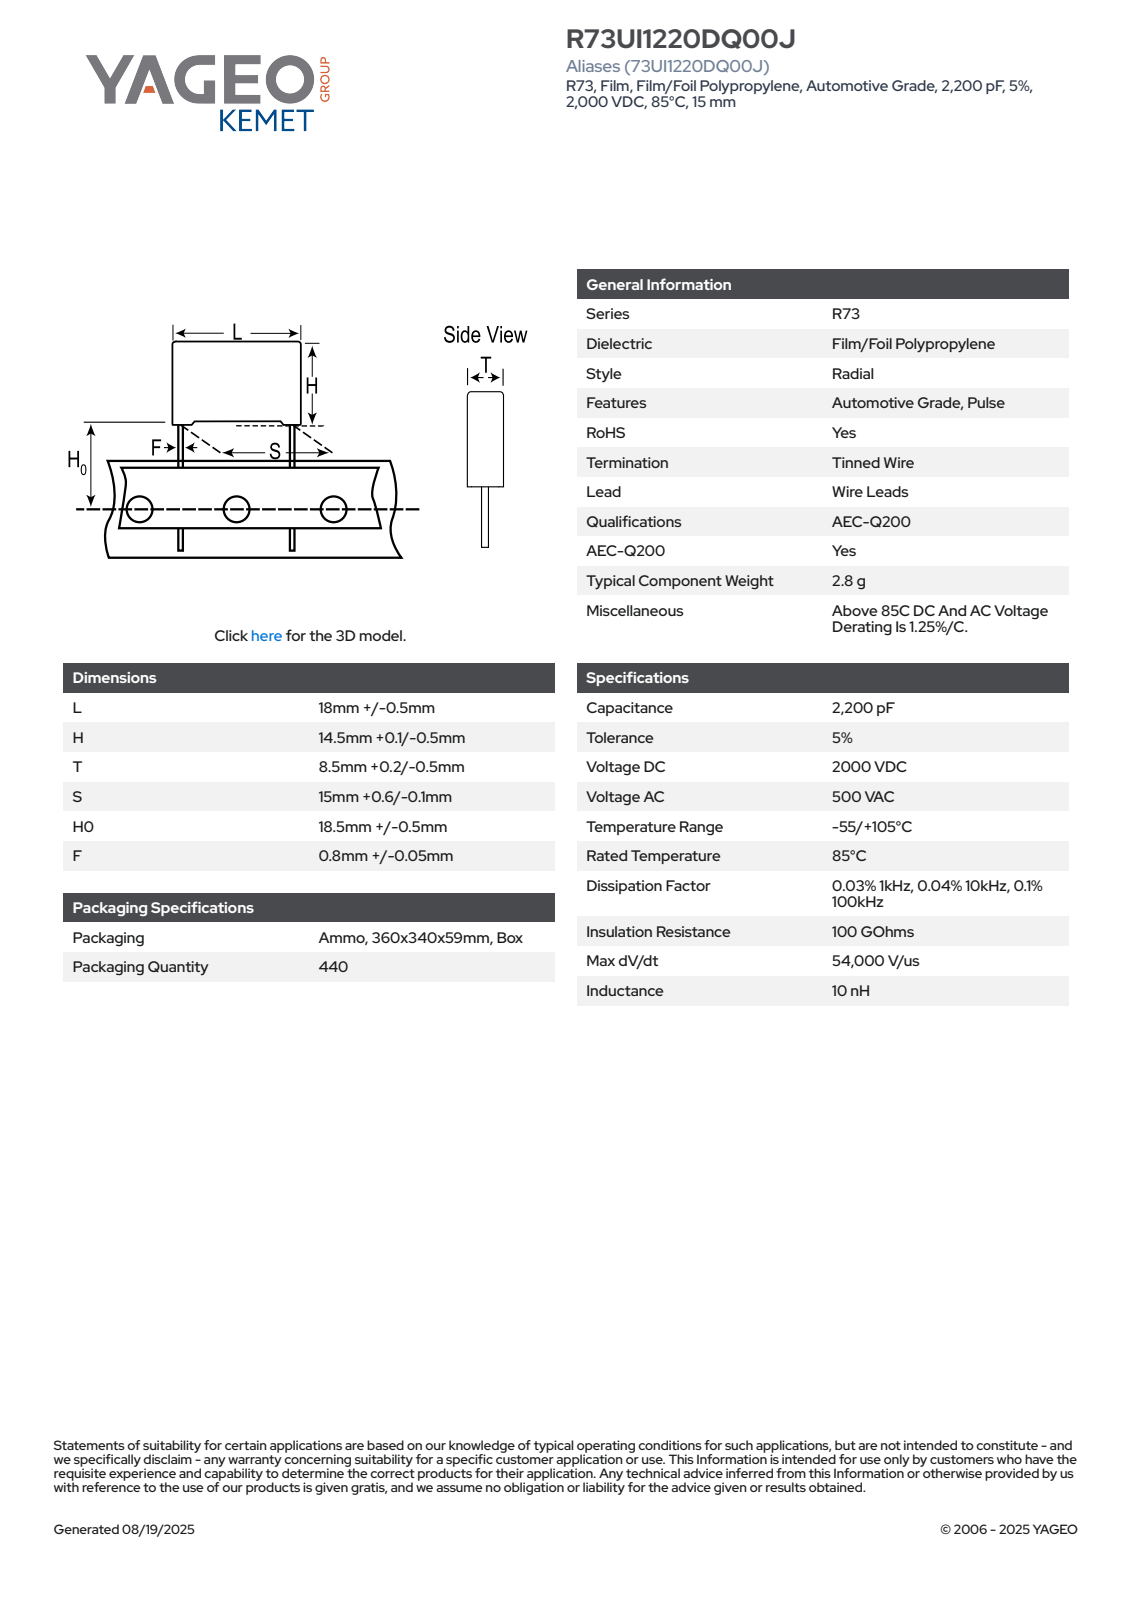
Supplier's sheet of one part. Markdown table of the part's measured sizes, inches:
| quantity | value |
| --- | --- |
| part name | CFR_RB2_18X14.5X8.5_L18.5H14.6T8.7S15H019F0.85 |
| STEP written by | SolidWorks 2020 (AUTOMOTIVE_DESIGN) |
| units | inches |
| bodies | 4 solids, 85 faces (77 planar, 8 cylindrical, 0 other) |
| overall size | 1.323 × 0.728 × 0.343 |
| volume | 0.138 in³ |
| surface area | 1.938 in² |
| round bosses / shafts (diameter × count) | 0.033 × 2 |
| partial cylindrical surfaces (radius × count) | 0.02 × 4 |
| main face-to-face distances | 0.343, 0.545, 0.728, 0.024, 0.03, 0.575, 0.318, 0.02, 0.555, 0.704 |
